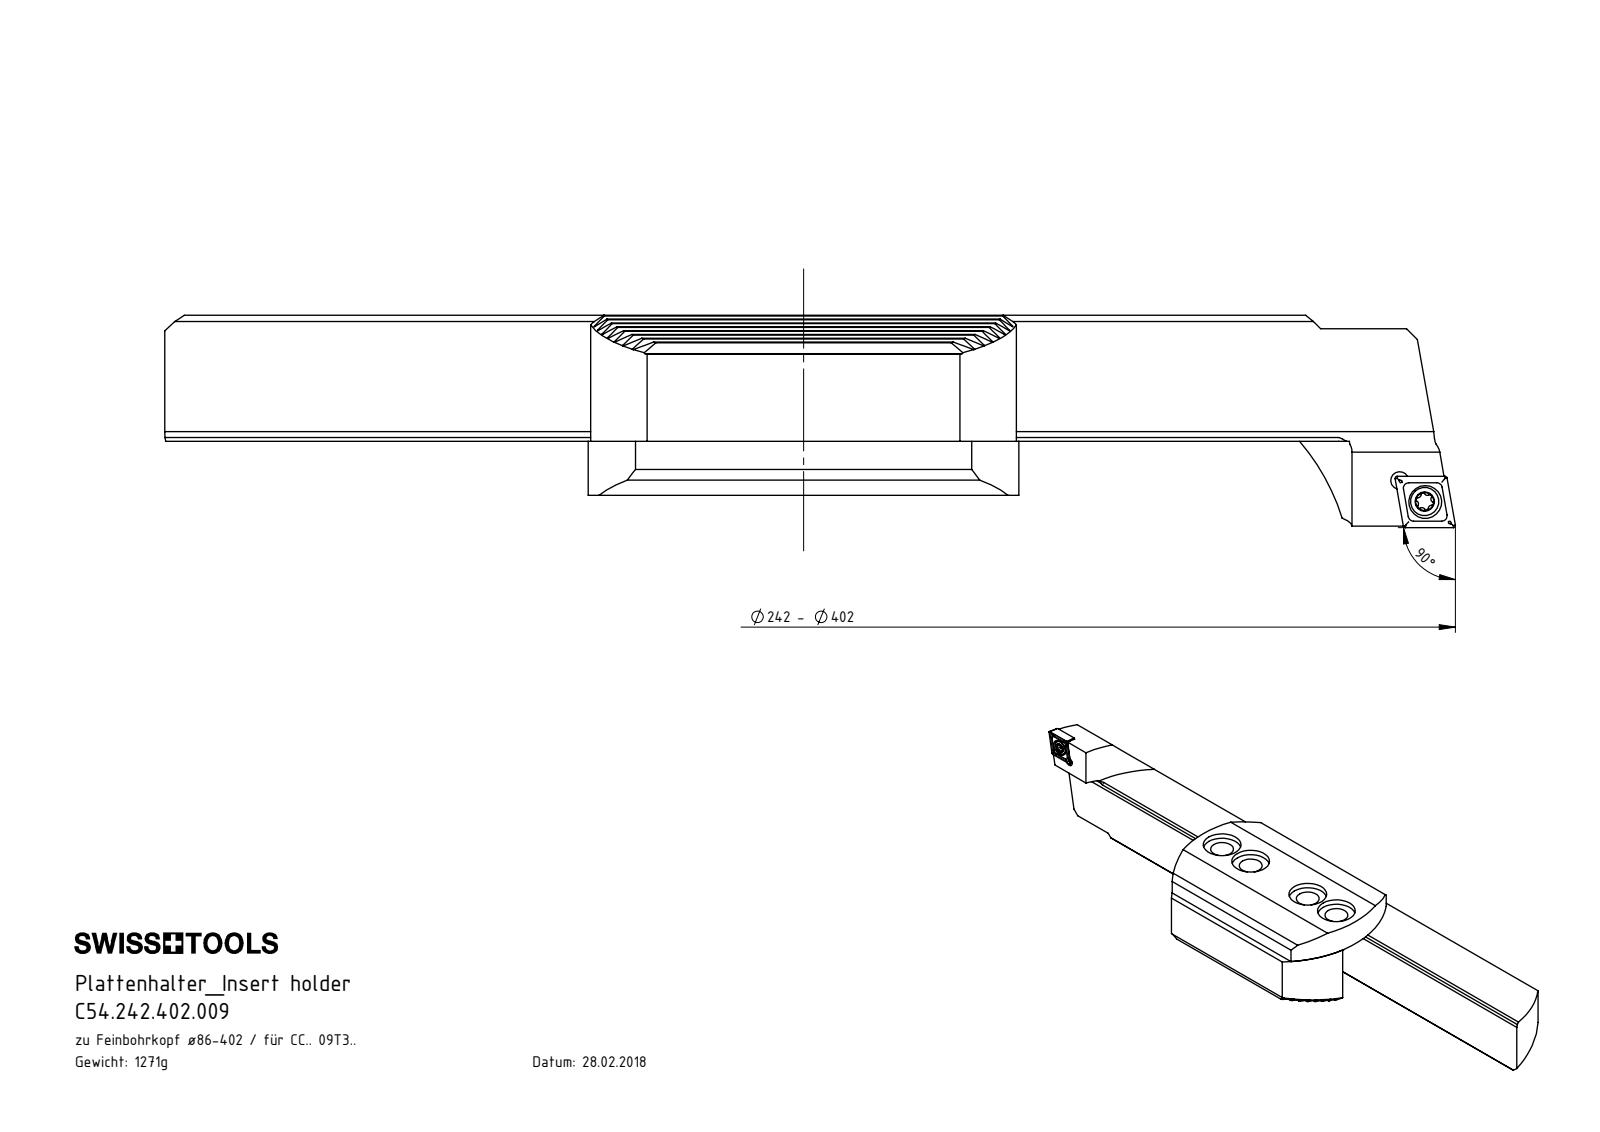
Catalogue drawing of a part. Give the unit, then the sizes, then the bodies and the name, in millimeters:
Units: millimetres
Overall size (bounding box): 239.57 × 55 × 39.4
Round holes (diameter × count): ⌀8.5 ×4, ⌀14 ×4, ⌀3.3 ×2, ⌀4.4 ×1, ⌀6.1 ×1
Round bosses / shafts (diameter × count): ⌀5.25 ×1, ⌀4 ×1
Partial cylindrical surfaces — rounded edges, fillets, slot ends (radius × count): R0.2 ×16, R0.34 ×6, R0.59 ×6, R40 ×6, R0.8 ×1
Main face-to-face distances: 2.38, 4.76, 21.3, 7.14, 33.7, 9.52, 4.77, 7.15, 9.53, 11.91
Hole centre spacings: 15, 45, 6.06, 6.19, 30, 60
Volume: 161 949 mm³ · Surface area: 41 929 mm²
Bodies: 5 solids, 992 faces (604 planar, 67 cylindrical, 321 other)
Part name (STEP PRODUCT): C54.242.402.009; F00-WCB.136.002_A; F00-WCB.136.003_A; F00-WCB.242.001 (+3 more)
STEP written by: SolidWorks 2017 (CONFIG_CONTROL_DESIGN)
